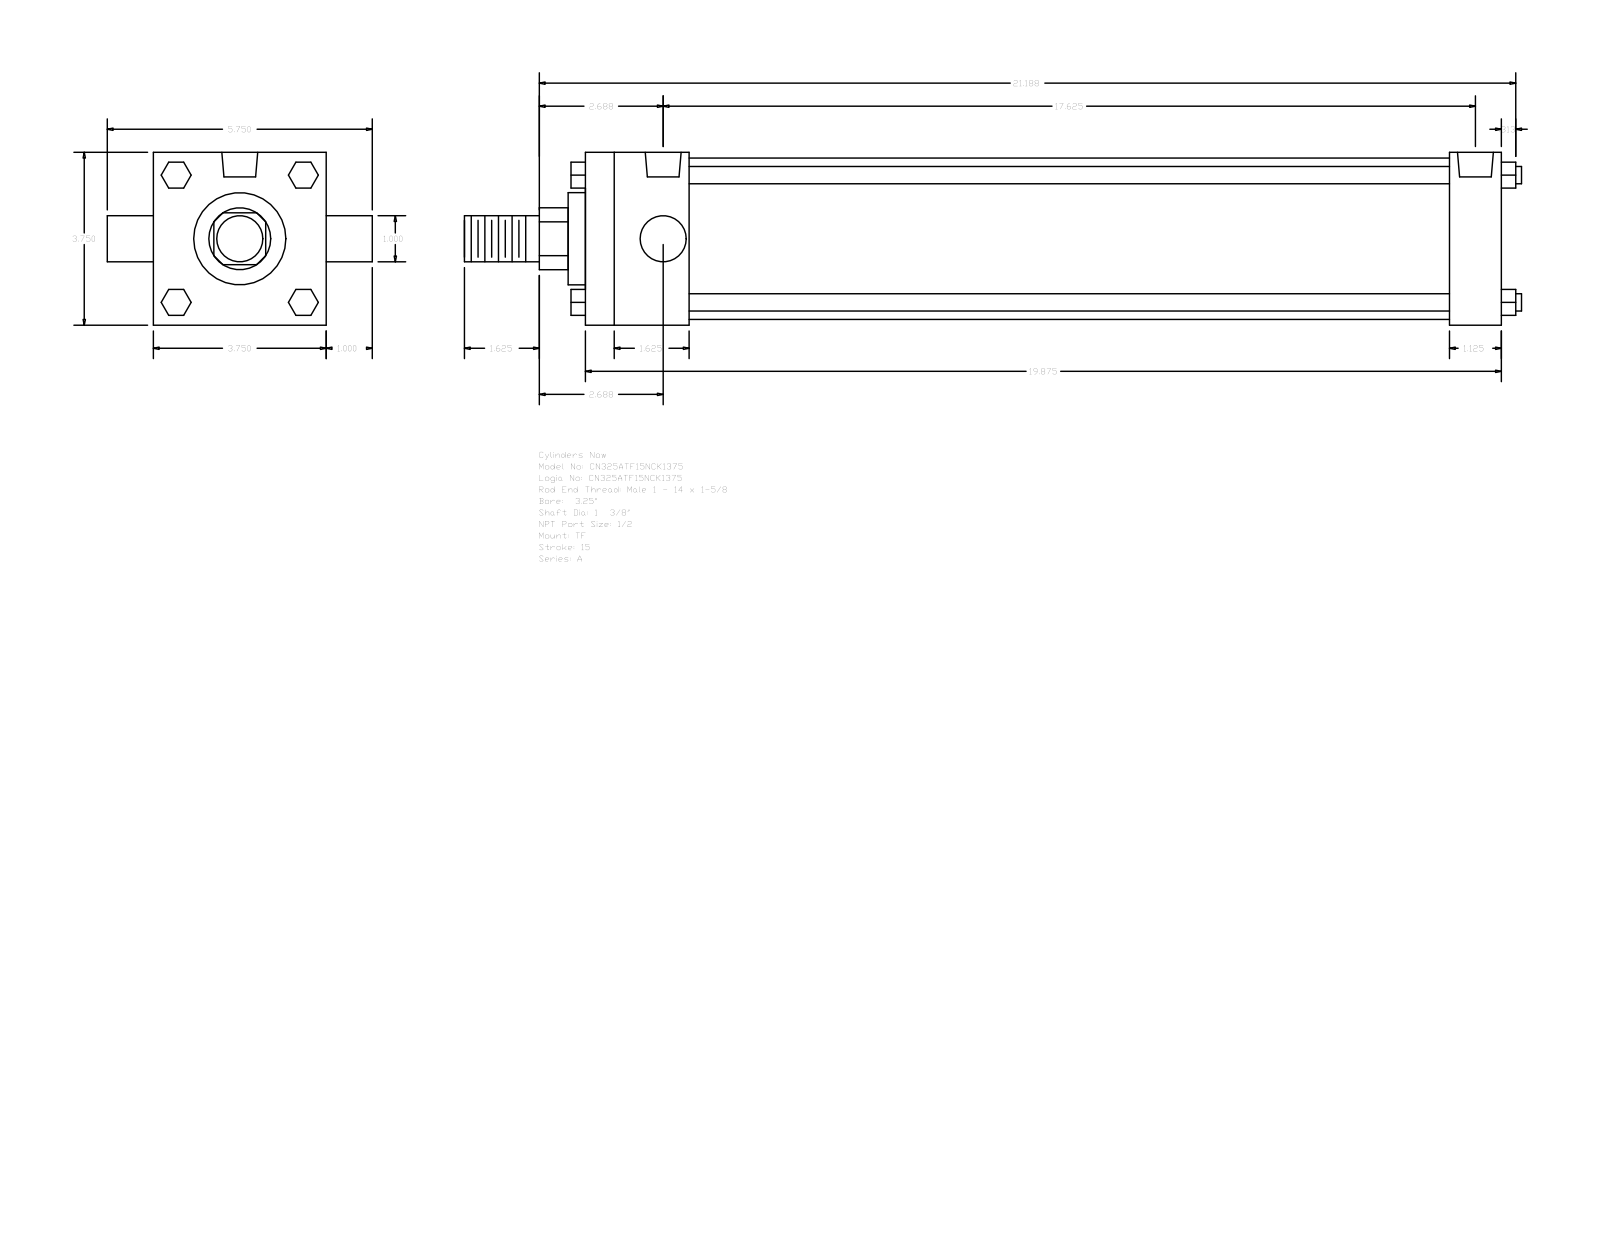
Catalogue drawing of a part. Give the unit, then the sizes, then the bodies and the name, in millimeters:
Units: millimetres
Overall size (bounding box): 582.61 × 146.05 × 95.25
Round holes (diameter × count): ⌀8.73 ×3, ⌀19.77 ×2
Round bosses / shafts (diameter × count): ⌀9.53 ×4, ⌀25.4 ×2, ⌀88.9 ×1, ⌀50.8 ×1, ⌀34.92 ×1
Partial cylindrical surfaces — rounded edges, fillets, slot ends (radius × count): R17.06 ×1
Main face-to-face distances: 95.24, 504.83, 57.15, 28.58, 476.25, 419.1, 447.68, 66.67, 9.52, 485.77
Hole centre spacings: 3.18, 444.5, 441.32, 447.68
Bodies: 0 solids, 120 faces (92 planar, 28 cylindrical, 0 other)
Part name (STEP PRODUCT): A_TF__0325_1.375
STEP written by: GSSL Pune (CONFIG_CONTROL_DESIGN)
